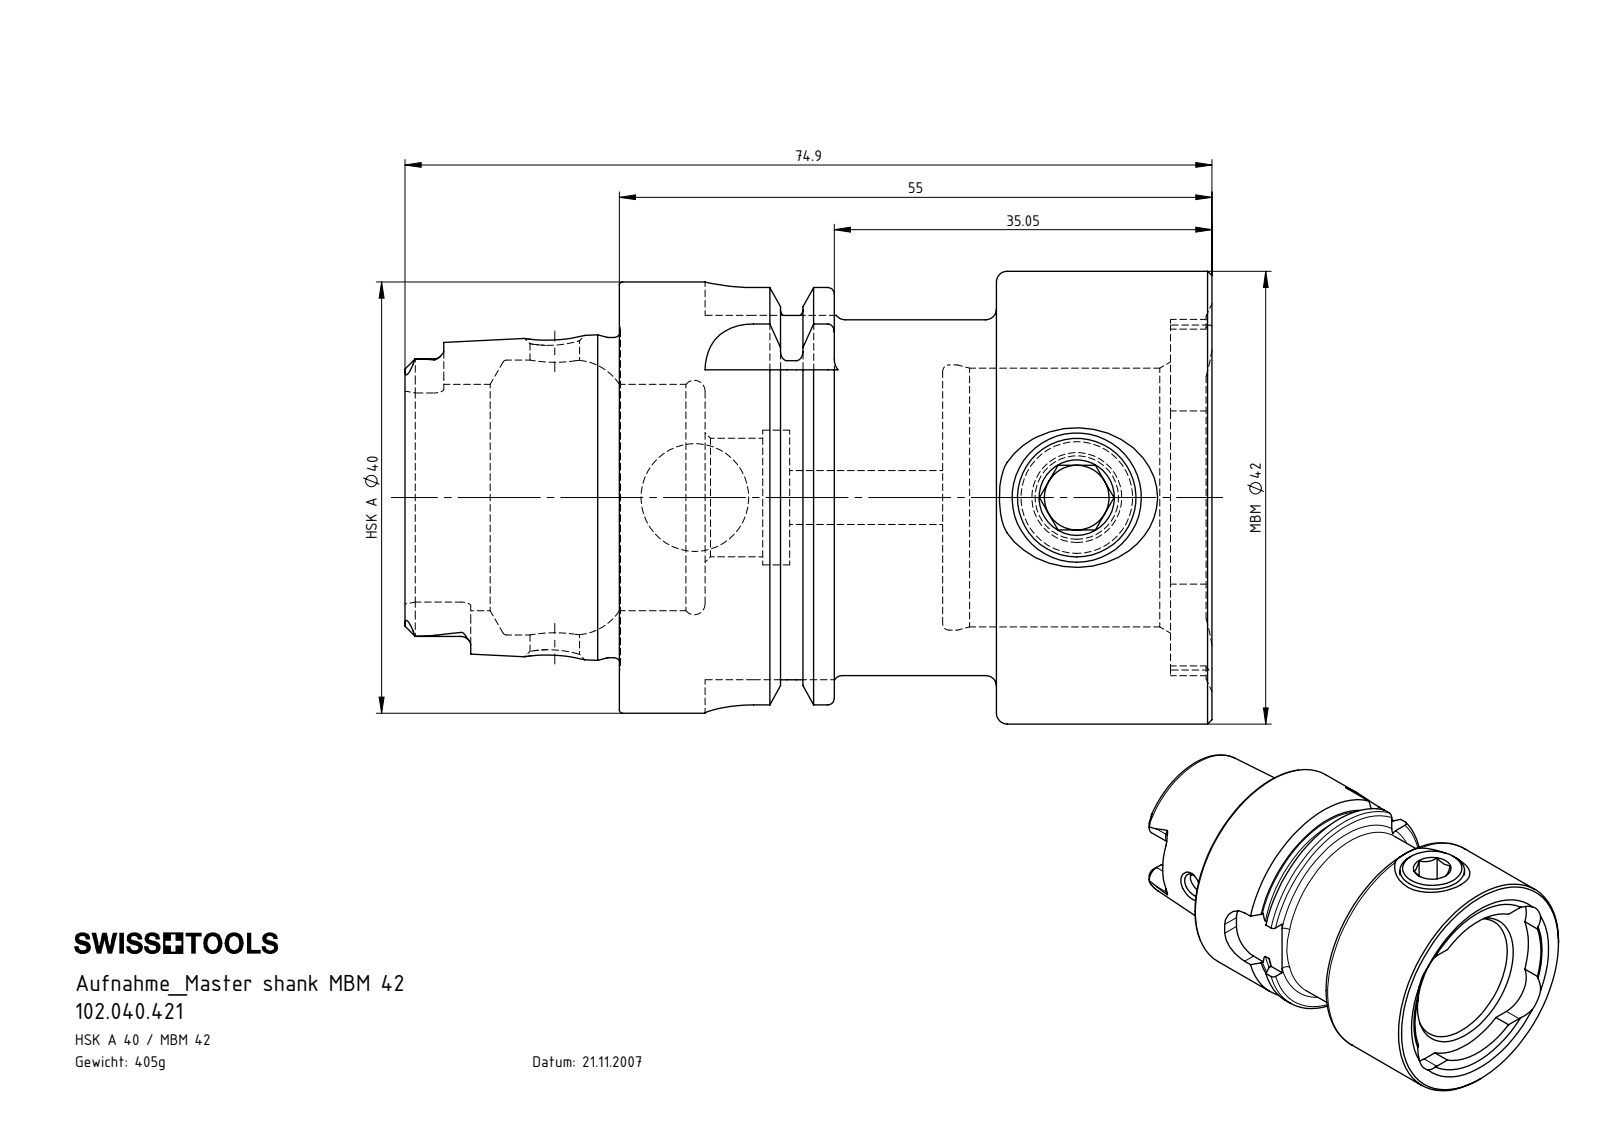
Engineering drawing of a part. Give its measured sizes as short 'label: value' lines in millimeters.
name: HA4-MB4.K01.055_A_Fertigbearbeitung; MB4-ER1.001.013_A; HA4.MB4.K01.055
written by: SolidWorks 2012 (CONFIG_CONTROL_DESIGN)
unit: mm
bodies: 2 solids, 224 faces (65 planar, 67 cylindrical, 92 other)
size: 74.9 × 42 × 42
volume: 51 636 mm³; area: 17 614 mm²
holes: 2× ⌀11, 1× ⌀4.6, 1× ⌀5, 1× ⌀10, 1× ⌀12.5, 1× ⌀21, 1× ⌀24, 1× ⌀24.6, 1× ⌀25.5
bosses: 1× ⌀42, 1× ⌀40, 1× ⌀34.75, 1× ⌀33, 1× ⌀29.71, 1× ⌀12
rounds: 6× R0.9, 4× R1.88, 4× R4.5, 4× R5.2, 1× R14.9, 1× R16.52
face distances: 30, 51.15, 21.15, 55, 25, 3.85, 35, 5, 16.15, 20
hole spacings: 35.45
